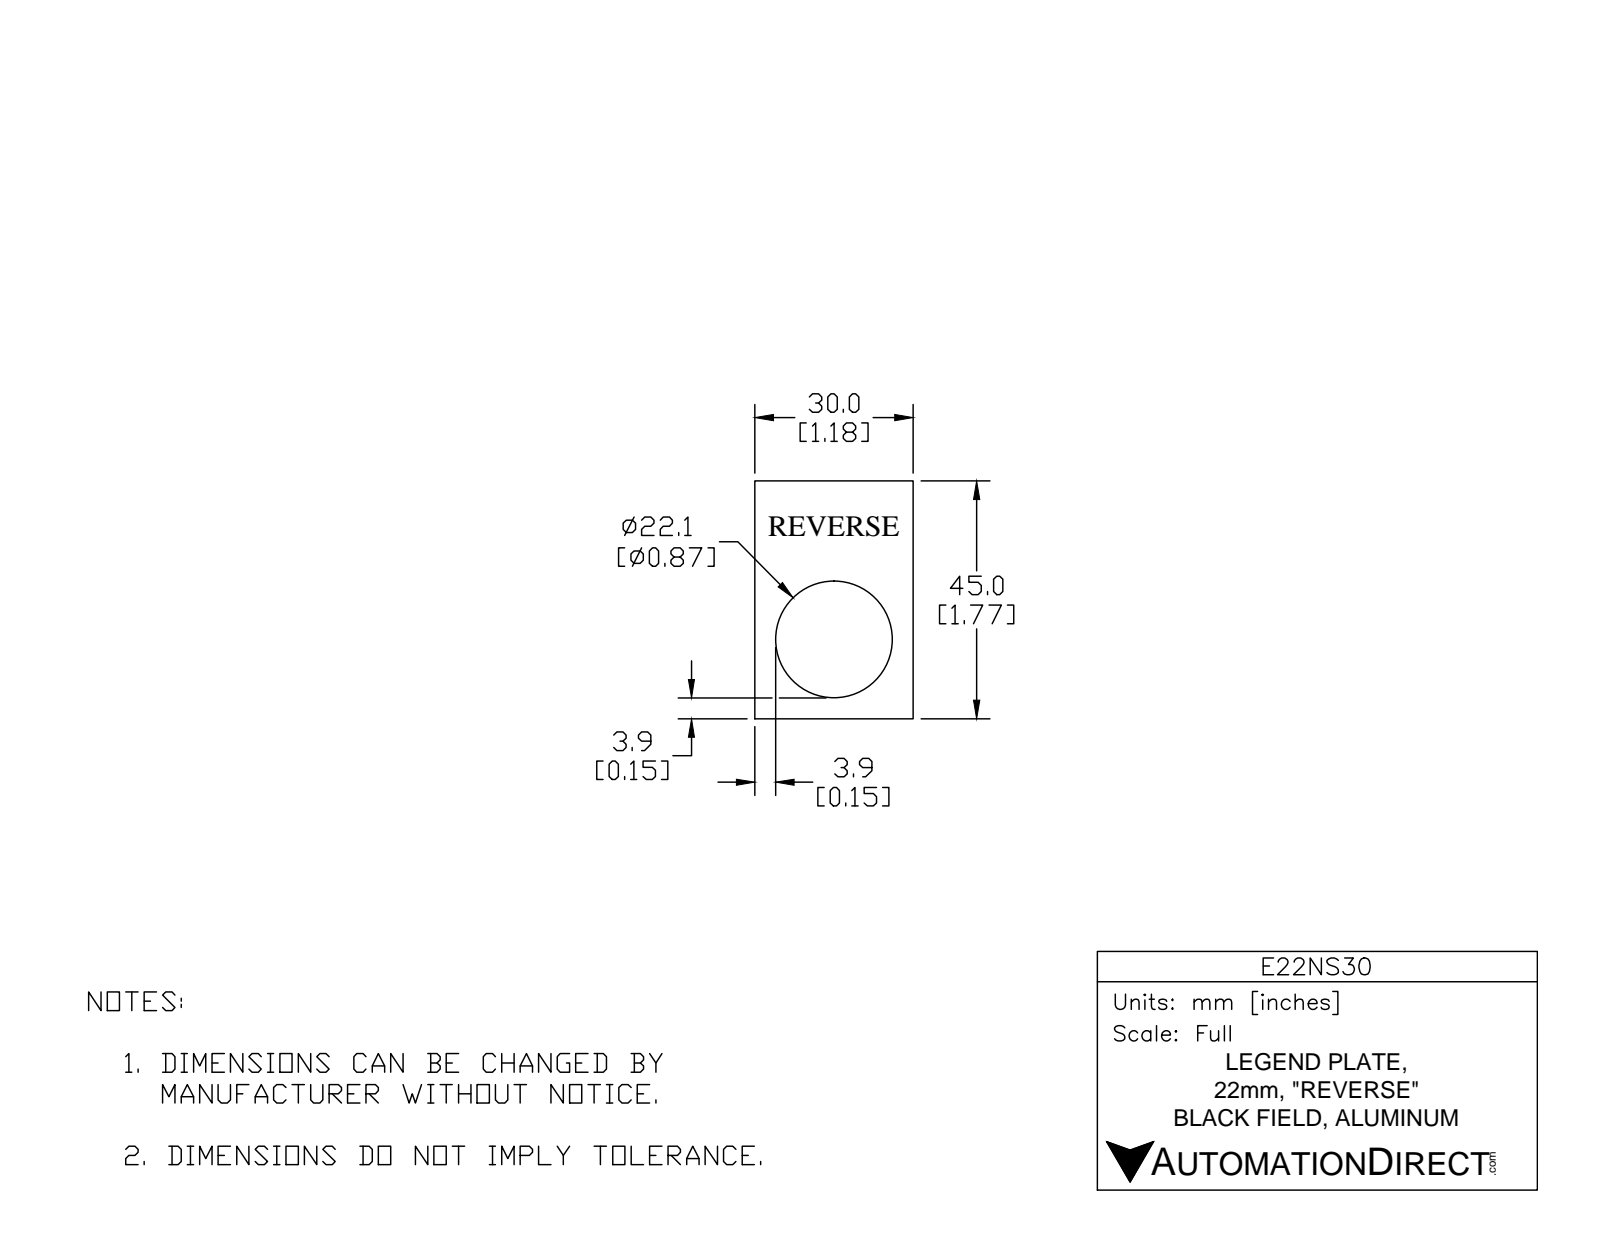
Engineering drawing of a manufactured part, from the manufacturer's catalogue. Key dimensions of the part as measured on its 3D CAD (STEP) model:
Part name (STEP PRODUCT): E22NS30
STEP written by: SolidWorks 2017 (AUTOMOTIVE_DESIGN)
Units: millimetres
Bodies: 1 solid, 113 faces (85 planar, 3 cylindrical, 25 other)
Overall size (bounding box): 45 × 30 × 1.3
Volume: 1 249 mm³ · Surface area: 2 253 mm²
Round holes (diameter × count): ⌀22.2 ×1
Main face-to-face distances: 1.3, 30, 45, 1.05, 0.41, 4.7, 40.3, 0.36, 3.59, 0.35
